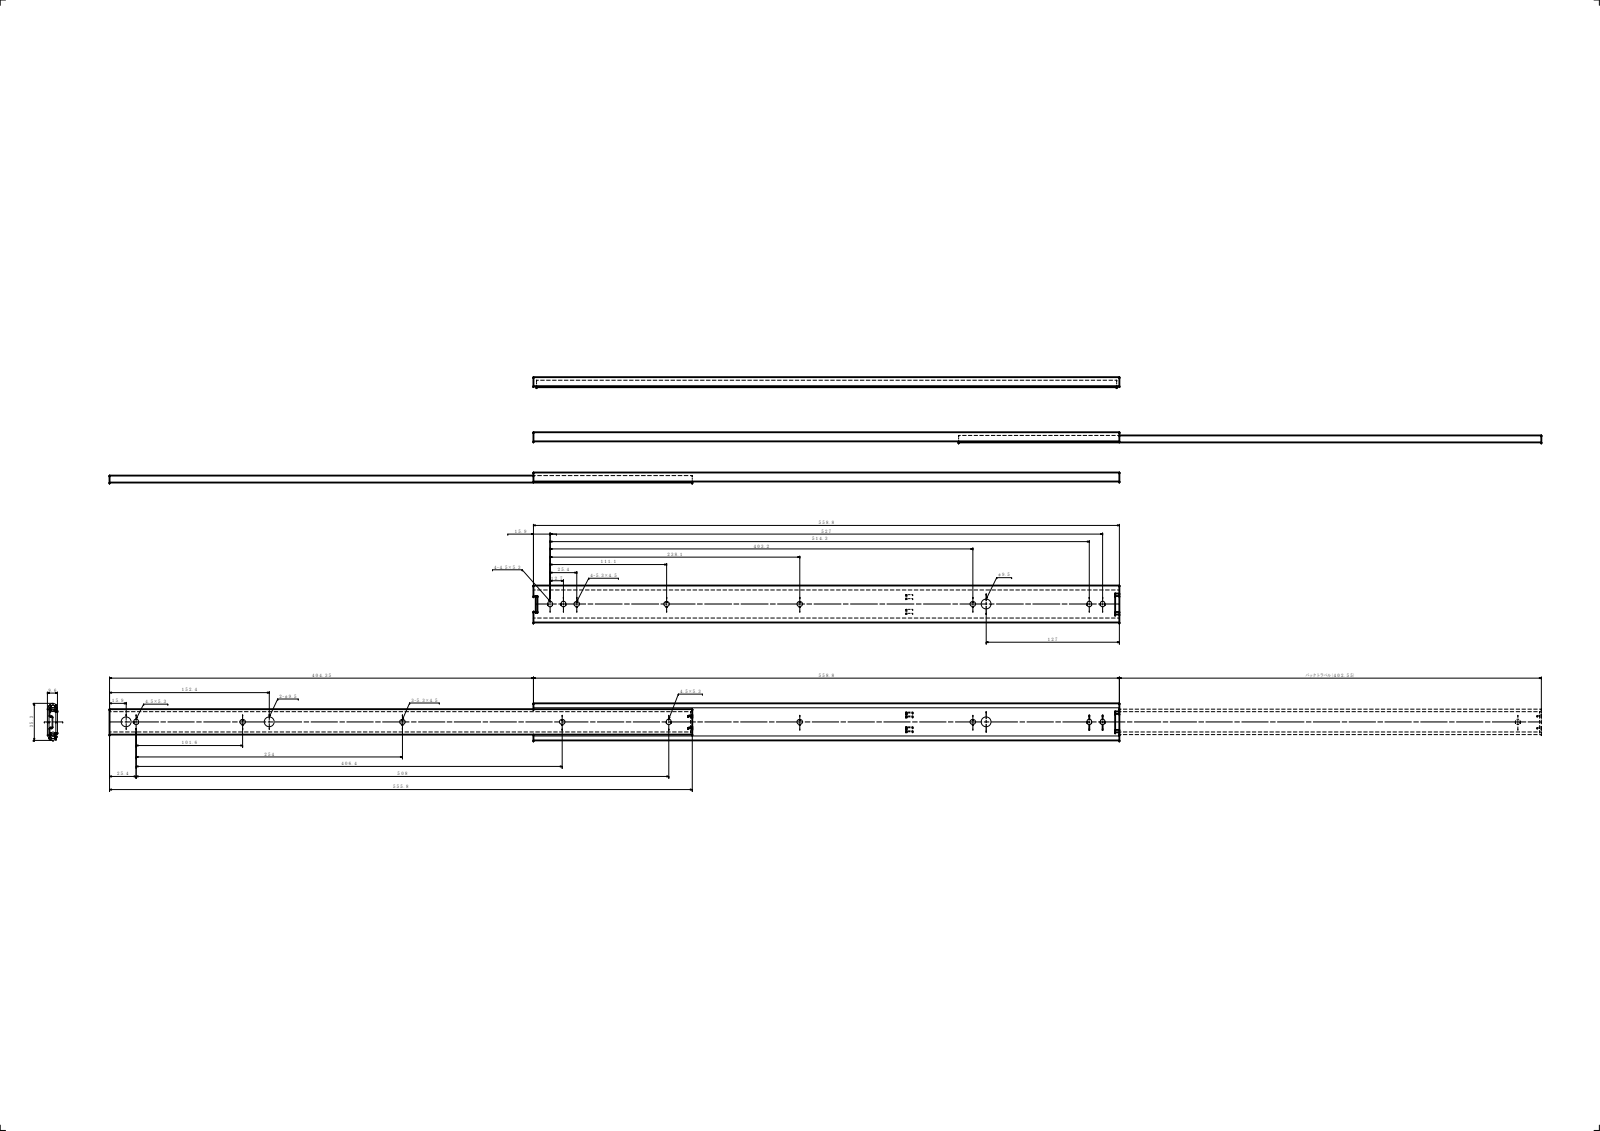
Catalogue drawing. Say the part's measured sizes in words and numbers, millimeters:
The part is named "IM 3521-22; OM 3520-22; 3520-22". Its 3-D file was written by "SolidWorks 2019 (CONFIG_CONTROL_DESIGN)". It is 2 solids with 147 faces: 72 planar, 75 cylindrical and 0 other. Overall it measures 964.35 by 35.3 by 9.6 millimeters. Its volume is 69 940 cubic millimeters and its surface area 91 749 square millimeters. Round holes: 3 of diameter 9.5. Partial cylindrical surfaces (rounded edges, fillets, slot ends): 26 of radius 2.25, 6 of radius 0.4, 4 of radius 1, 4 of radius 2.5, 4 of radius 3, 2 of radius 0.2, 2 of radius 1.8, 2 of radius 2. The main face-to-face distances are 1.6, 8, 9.6, 6.4, 1.3, 6.7, 4.67, 3.07, 2.9, 5.1. The hole center spacings are 136.5, 684.95, 821.45.
